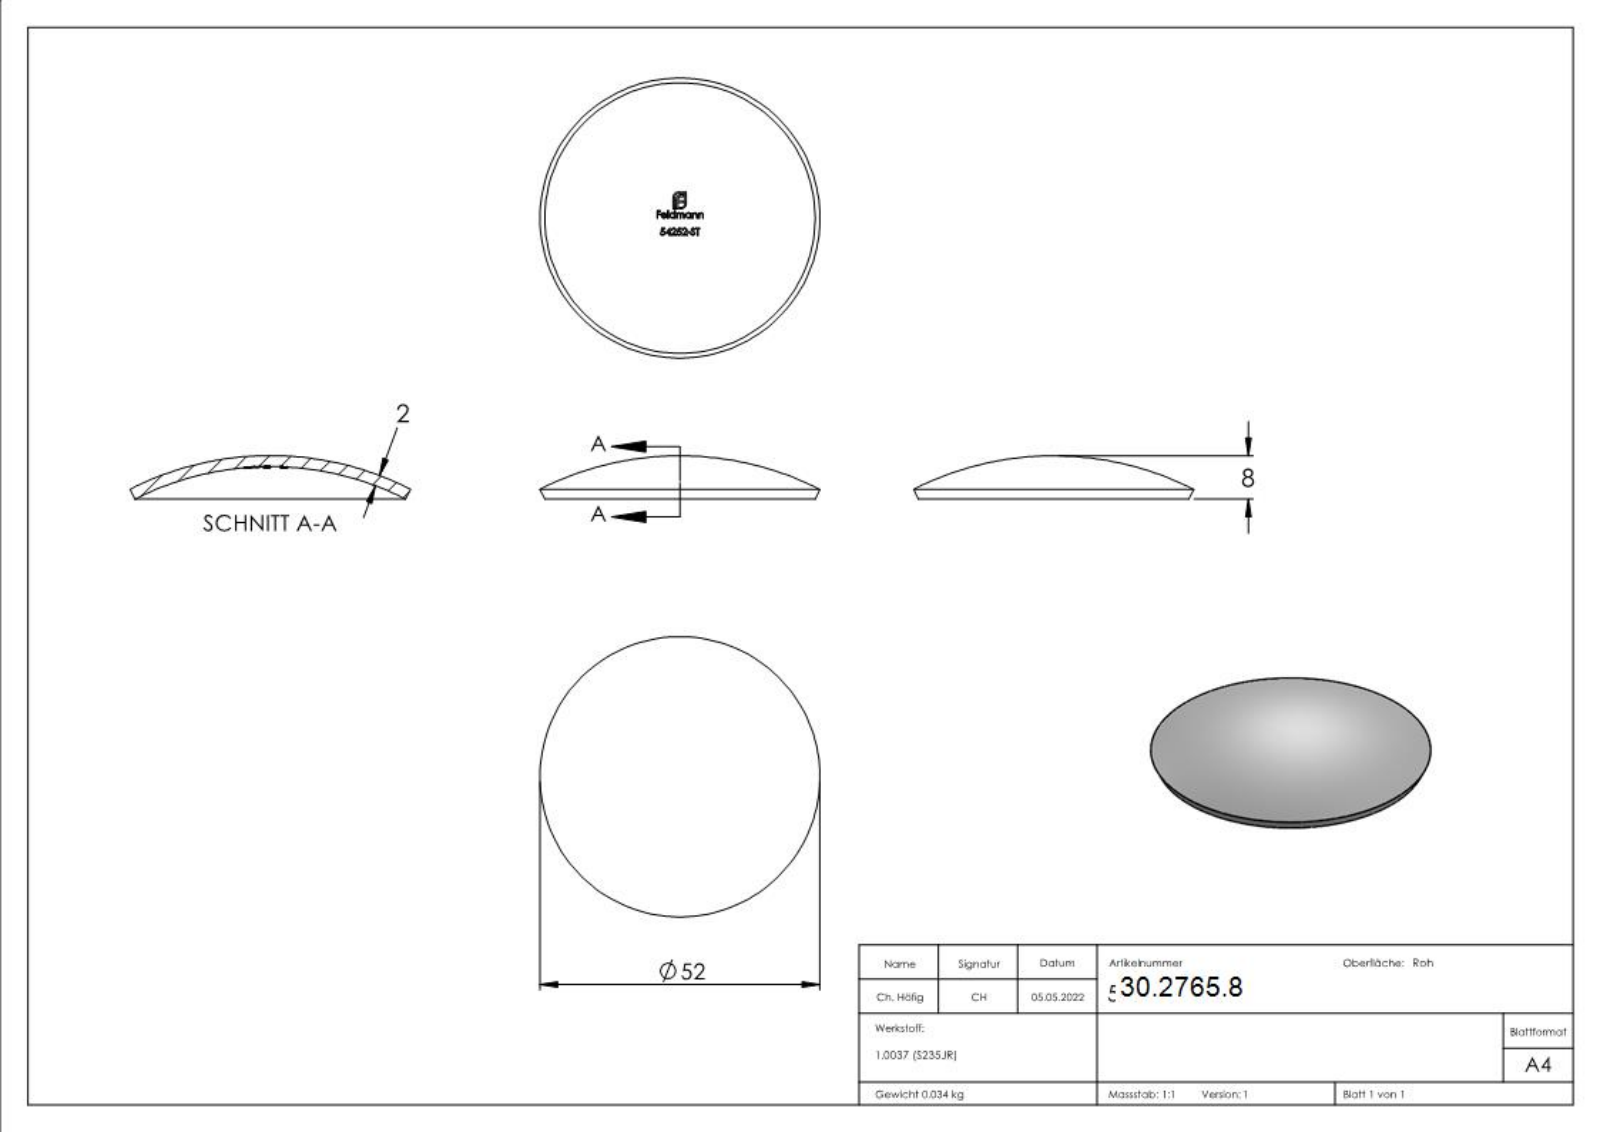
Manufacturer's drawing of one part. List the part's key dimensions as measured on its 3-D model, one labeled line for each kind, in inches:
Part name (STEP PRODUCT): 54252-ST
STEP written by: SolidWorks 2018 (CONFIG_CONTROL_DESIGN)
Units: inches
Bodies: 1 solid, 262 faces (127 planar, 0 cylindrical, 135 other)
Overall size (bounding box): 2.047 × 2.047 × 0.315
Volume: 0.265 in³ · Surface area: 7.237 in²
Main face-to-face distances: 0.167, 0.05, 0.045, 0.047, 0.039, 0.025, 0.023, 0.052, 0.013, 0.08
